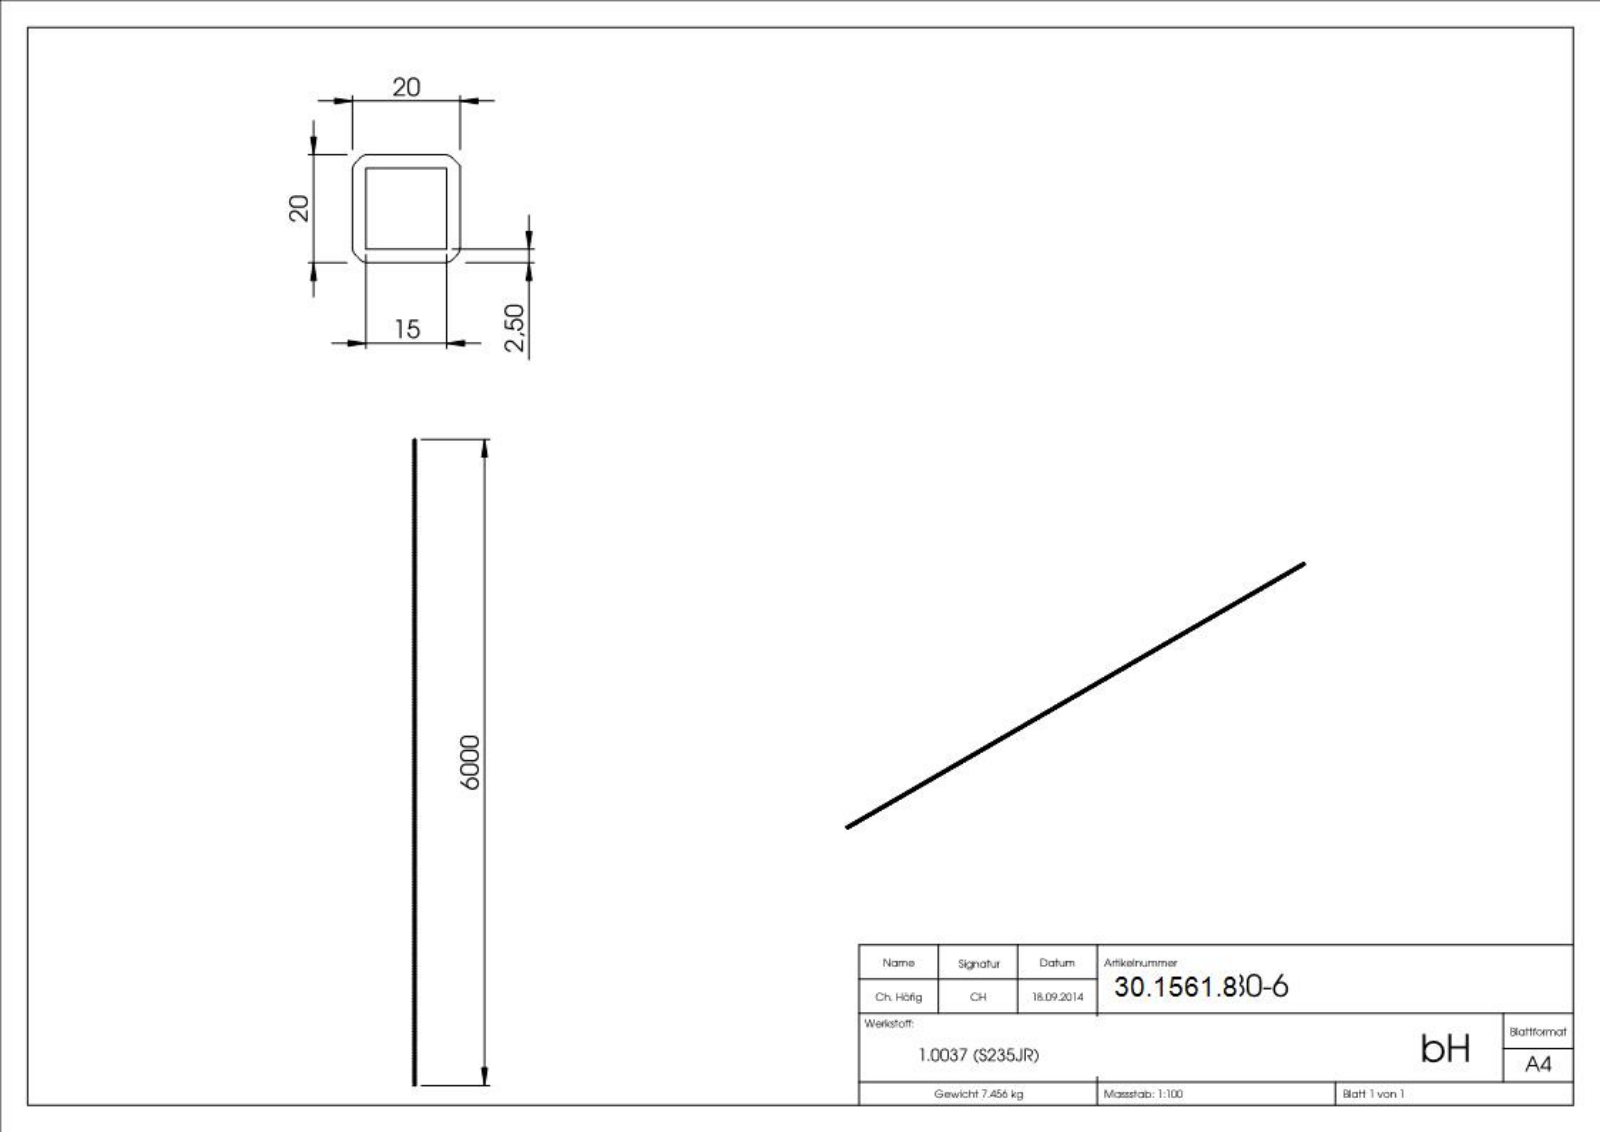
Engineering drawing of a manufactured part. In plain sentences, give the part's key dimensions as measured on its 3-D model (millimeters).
The part is named "6980-6". Its 3-D file was written by "SolidWorks 2018 (CONFIG_CONTROL_DESIGN)". It is 1 solid with 4813 faces: 102 planar, 2306 cylindrical and 2405 other. Overall it measures 6000 by 20 by 20 millimeters. Its volume is 808 558 cubic millimeters and its surface area 815 276 square millimeters. Partial cylindrical surfaces (rounded edges, fillets, slot ends): 4 of radius 1, 4 of radius 3. The main face-to-face distances are 2, 18, 20, 16, 6000, 5500, 500, 1.9, 16.1, 18.1.
